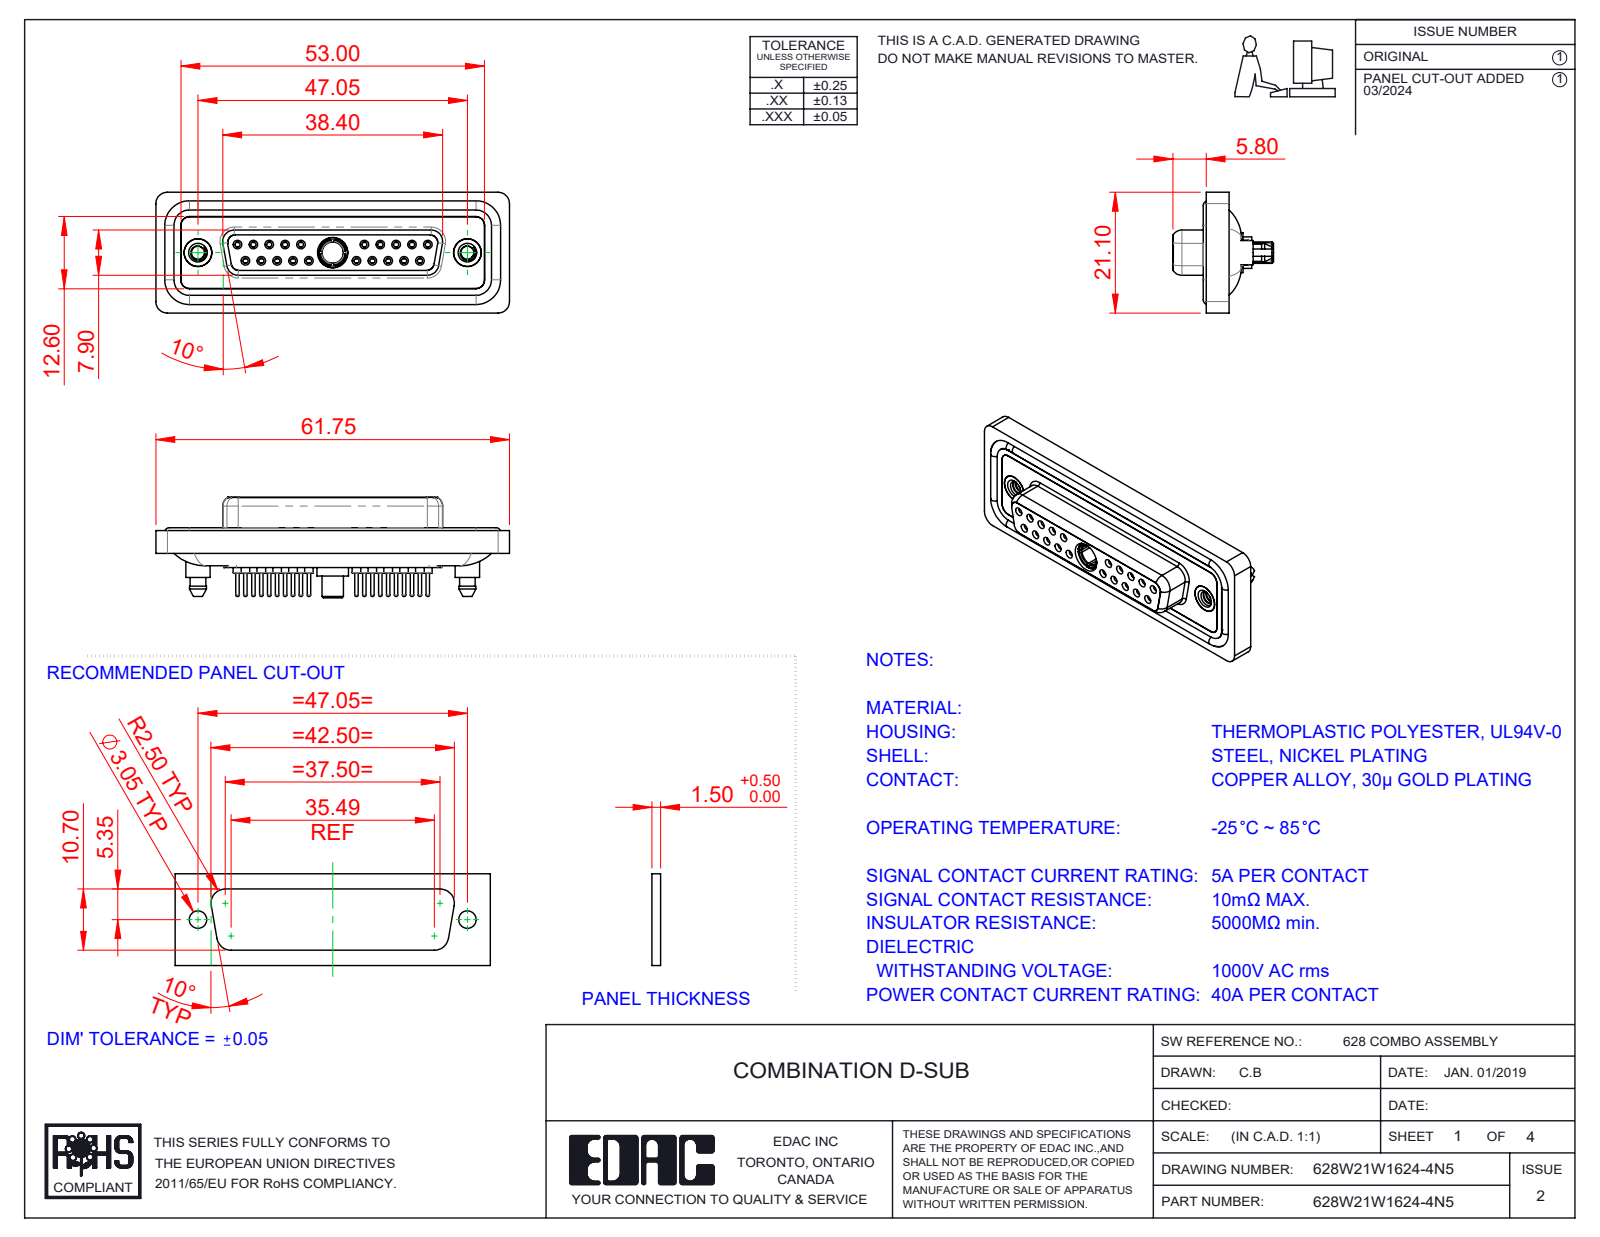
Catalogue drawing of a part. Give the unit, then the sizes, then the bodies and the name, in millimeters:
Units: millimetres
Overall size (bounding box): 61.75 × 21.1 × 17.55
Round holes (diameter × count): ⌀0.9 ×20, ⌀1.1 ×20, ⌀1.5 ×20, ⌀2 ×20, ⌀1.6 ×10, ⌀1.7 ×10, ⌀4.85 ×3, ⌀2.26 ×2, ⌀4 ×2, ⌀4.05 ×2, ⌀5 ×2, ⌀3.7 ×1
Round bosses / shafts (diameter × count): ⌀2.2 ×20, ⌀0.6 ×20, ⌀1.6 ×14, ⌀5.4 ×2, ⌀4.95 ×2, ⌀4.8 ×2, ⌀4.25 ×2, ⌀5.5 ×1
Partial cylindrical surfaces — rounded edges, fillets, slot ends (radius × count): R1.5 ×24, R2 ×18, R1.6 ×10, R1.35 ×8, R0.25 ×4, R0.5 ×4, R0.6 ×4, R0.65 ×4
Main face-to-face distances: 0.4, 1.8, 7.45, 6.6, 5.65, 1.6, 0.5, 7.05, 2.9, 1.1
Hole centre spacings: 3.16, 2.77, 5.54, 5.03, 8.31, 7.48, 16.62, 19.39
Volume: 8 526 mm³ · Surface area: 14 346 mm²
Bodies: 29 solids, 1610 faces (450 planar, 623 cylindrical, 537 other)
Part name (STEP PRODUCT): 628Combo Shell Front_25 Contacts; Power Socket_40A S; 628W21W1624-4N5; 628Combo Housing_21W1 (+5 more)
STEP written by: SolidWorks 2023 (CONFIG_CONTROL_DESIGN)
